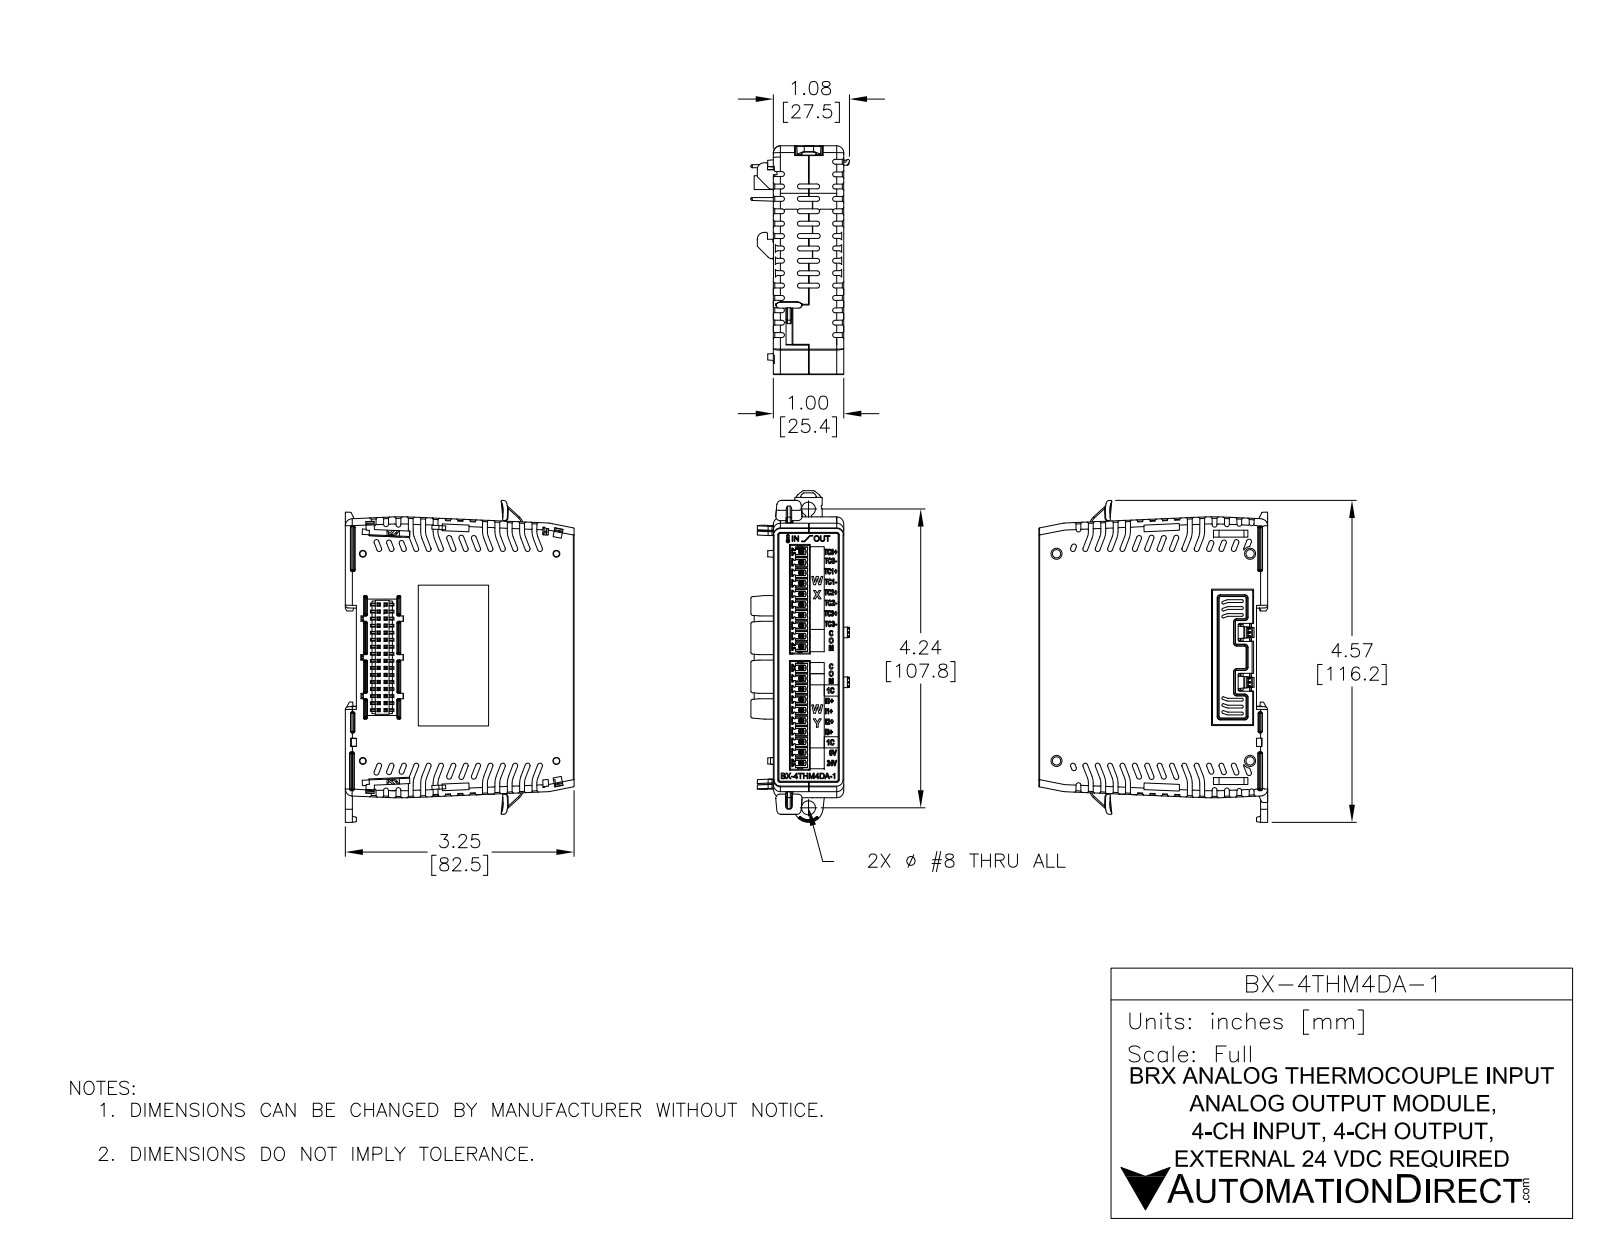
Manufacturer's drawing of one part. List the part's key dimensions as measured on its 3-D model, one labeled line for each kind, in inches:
Part name (STEP PRODUCT): BX-4THM4DA-1
STEP written by: SolidWorks 2017 (AUTOMOTIVE_DESIGN)
Units: inches
Bodies: 24 solids, 4932 faces (3505 planar, 636 cylindrical, 791 other)
Overall size (bounding box): 4.586 × 3.25 × 1.401
Volume: 9.457 in³ · Surface area: 89.4 in²
Round holes (diameter × count): ⌀0.016 ×8, ⌀0.016 ×2, ⌀0.118 ×2, ⌀0.118 ×2, ⌀0.04 ×1, ⌀0.199 ×1
Round bosses / shafts (diameter × count): ⌀0.111 ×2, ⌀0.059 ×2, ⌀0.071 ×1, ⌀0.044 ×1, ⌀0.036 ×1
Partial cylindrical surfaces — rounded edges, fillets, slot ends (radius × count): R0.02 ×109, R0.008 ×103, R0.005 ×48, R0.062 ×20, R0.012 ×16, R0.014 ×16, R0.01 ×14, R0.008 ×12
Main face-to-face distances: 1, 0.835, 0.165, 3.053, 0.209, 0.627, 0.791, 3.063, 2.053, 1.01
Hole centre spacings: 0.15, 0.3, 0.45, 0.6, 0.75, 1.651, 0.9, 1.501
